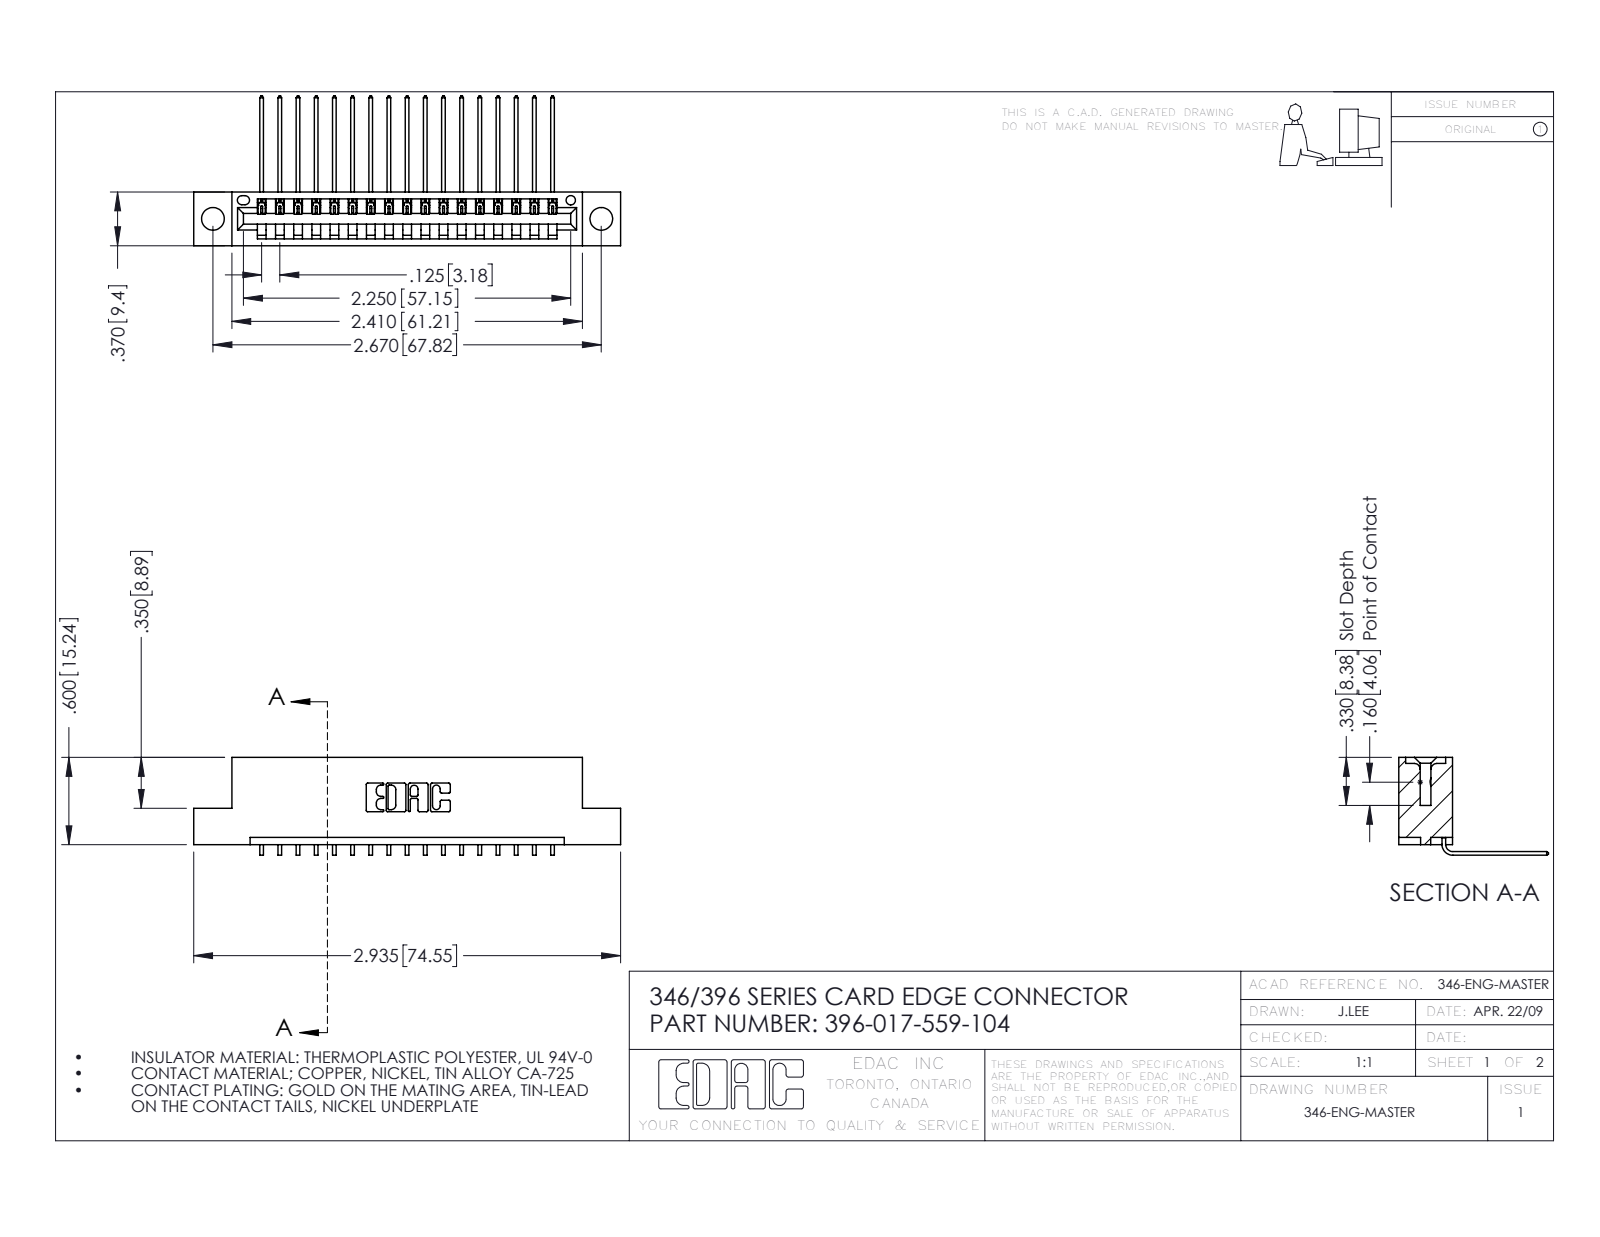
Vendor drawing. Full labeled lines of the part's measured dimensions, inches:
Part name (STEP PRODUCT): 345-292-001_558 559 Tail - 1; 346 Part_Flush Mounting Lugs - 0.156 Dia-TH; 396-017-559-104
STEP written by: SolidWorks 2016 (CONFIG_CONTROL_DESIGN)
Units: inches
Bodies: 18 solids, 1142 faces (790 planar, 352 cylindrical, 0 other)
Overall size (bounding box): 2.935 × 1.03 × 0.673
Volume: 0.423 in³ · Surface area: 13.23 in²
Round holes (diameter × count): ⌀0.156 ×2, ⌀0.064 ×1
Partial cylindrical surfaces — rounded edges, fillets, slot ends (radius × count): R0.006 ×34, R0.01 ×22, R0.007 ×6, R0.031 ×6, R0.026 ×3, R0.031 ×2, R0.04 ×2, R0.014 ×1
Main face-to-face distances: 0.048, 0.322, 0.37, 0.25, 0.072, 0.025, 0.298, 0.148, 0.222, 0.1
Hole centre spacings: 0.246, 2.463, 2.67
